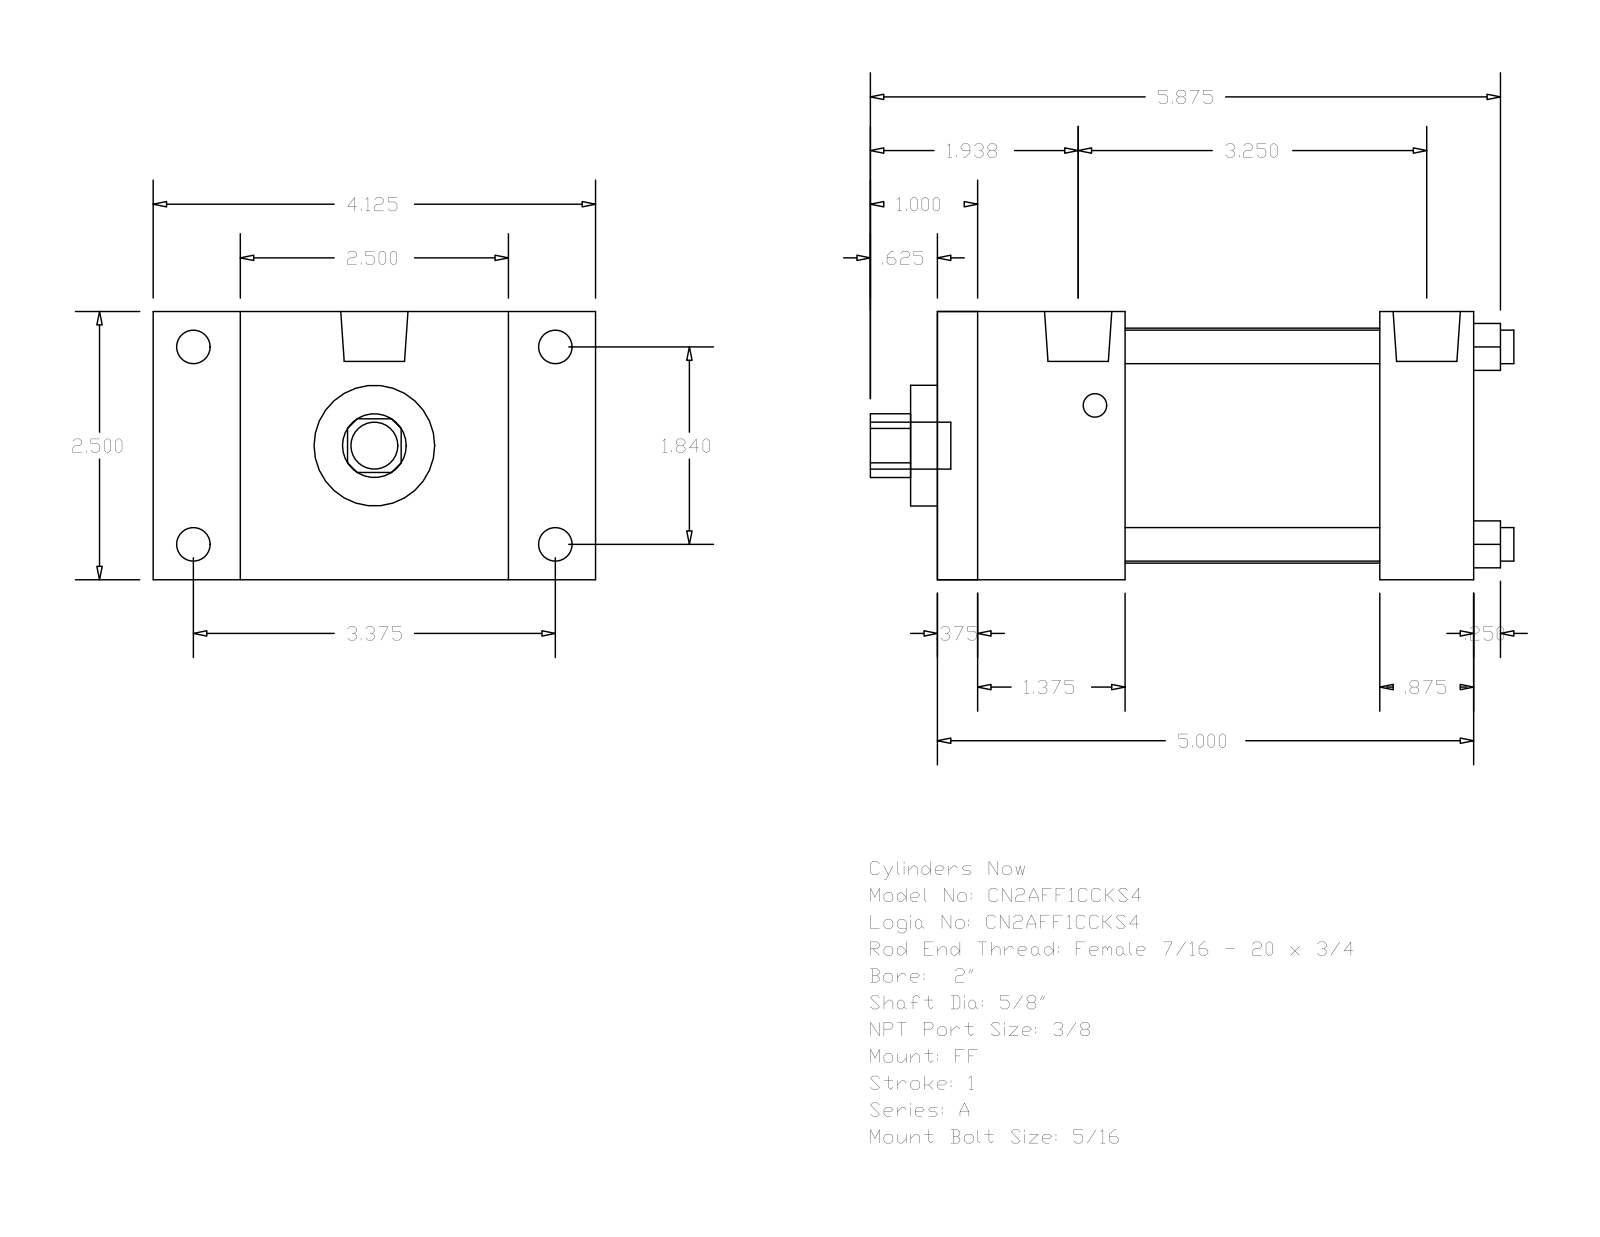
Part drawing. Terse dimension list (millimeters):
name: A_FF__0200_0.625
written by: GSSL Pune (CONFIG_CONTROL_DESIGN)
unit: mm
bodies: 0 solids, 92 faces (64 planar, 28 cylindrical, 0 other)
size: 152.4 × 104.78 × 63.5
holes: 4× ⌀7.94, 1× ⌀15.88, 1× ⌀28.57, 1× ⌀55.63
bosses: 4× ⌀7.94, 4× ⌀5.56, 2× ⌀15.93, 1× ⌀11.11
rounds: 1× R7.54
face distances: 63.5, 127, 9.52, 117.48, 44.45, 104.77, 34.93, 95.25, 60.32, 82.55
hole spacings: 33.05, 46.74, 66.1
